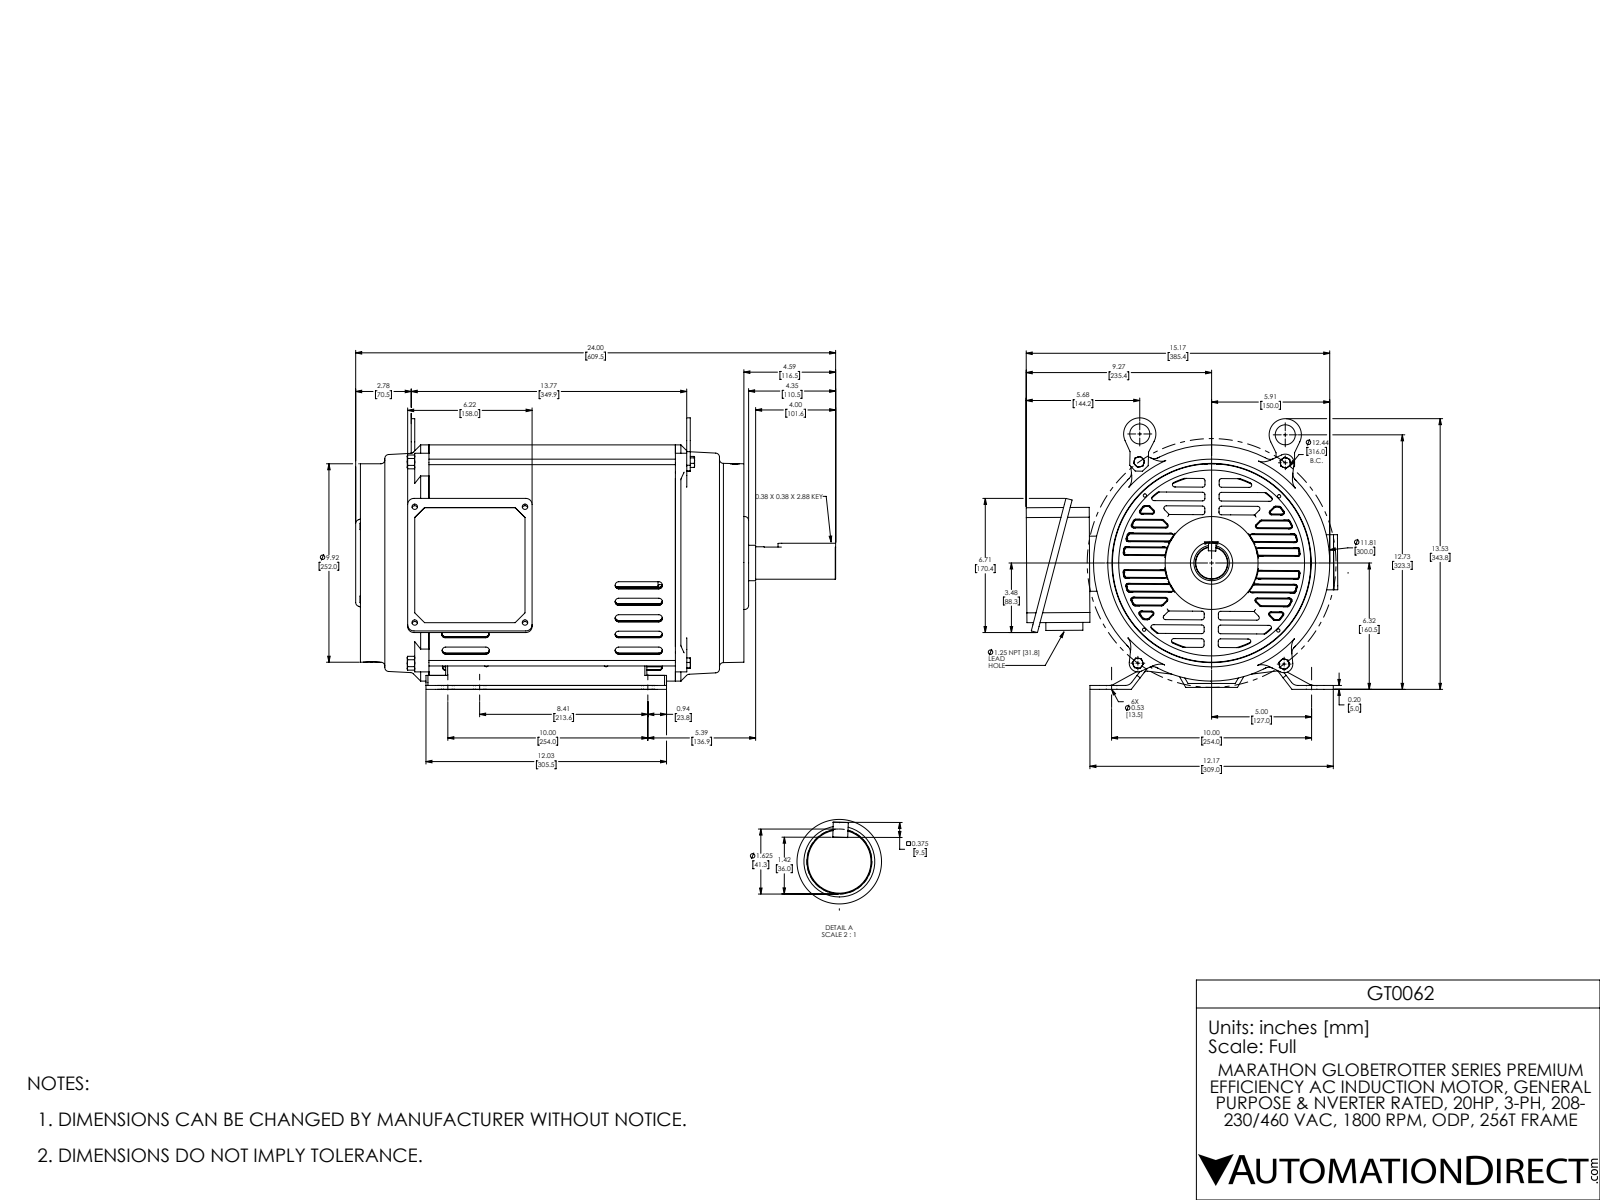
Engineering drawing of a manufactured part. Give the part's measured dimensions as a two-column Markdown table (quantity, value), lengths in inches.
| quantity | value |
| --- | --- |
| part name | SS620685-256T_RevA R1 Good Coord |
| STEP written by | SolidWorks 2017 (AUTOMOTIVE_DESIGN) |
| units | inches |
| bodies | 19 solids, 3000 faces (711 planar, 902 cylindrical, 1387 other) |
| overall size | 23.997 × 15.576 × 13.577 |
| volume | 550.3 in³ |
| surface area | 3 059 in² |
| round holes (diameter × count) | 0.374 × 20, 0.276 × 17, 0.531 × 12, 0.315 × 10, 0.165 × 4, 0.346 × 4, 0.5 × 4, 0.335 × 2, 0.787 × 2, 1.004 × 2, 1.319 × 2, 0.217 × 1 |
| round bosses / shafts (diameter × count) | 1.713 × 2, 11.811 × 1, 11.079 × 1, 4.331 × 1, 2.374 × 1, 2.165 × 1, 1.89 × 1, 1.85 × 1 |
| partial cylindrical surfaces (radius × count) | 0.079 × 135, 0.118 × 100, 0.197 × 77, 0.177 × 18, 0.394 × 18, 0.059 × 8, 0.295 × 8, 0.472 × 8 |
| main face-to-face distances | 0.197, 0.098, 0.295, 3.15, 0.984, 17.972, 3.661, 15.984, 15.551, 16.555 |
| hole center spacings | 0.099, 1.083, 5.984, 10, 1.531, 1.988, 2.008, 2.289 |
